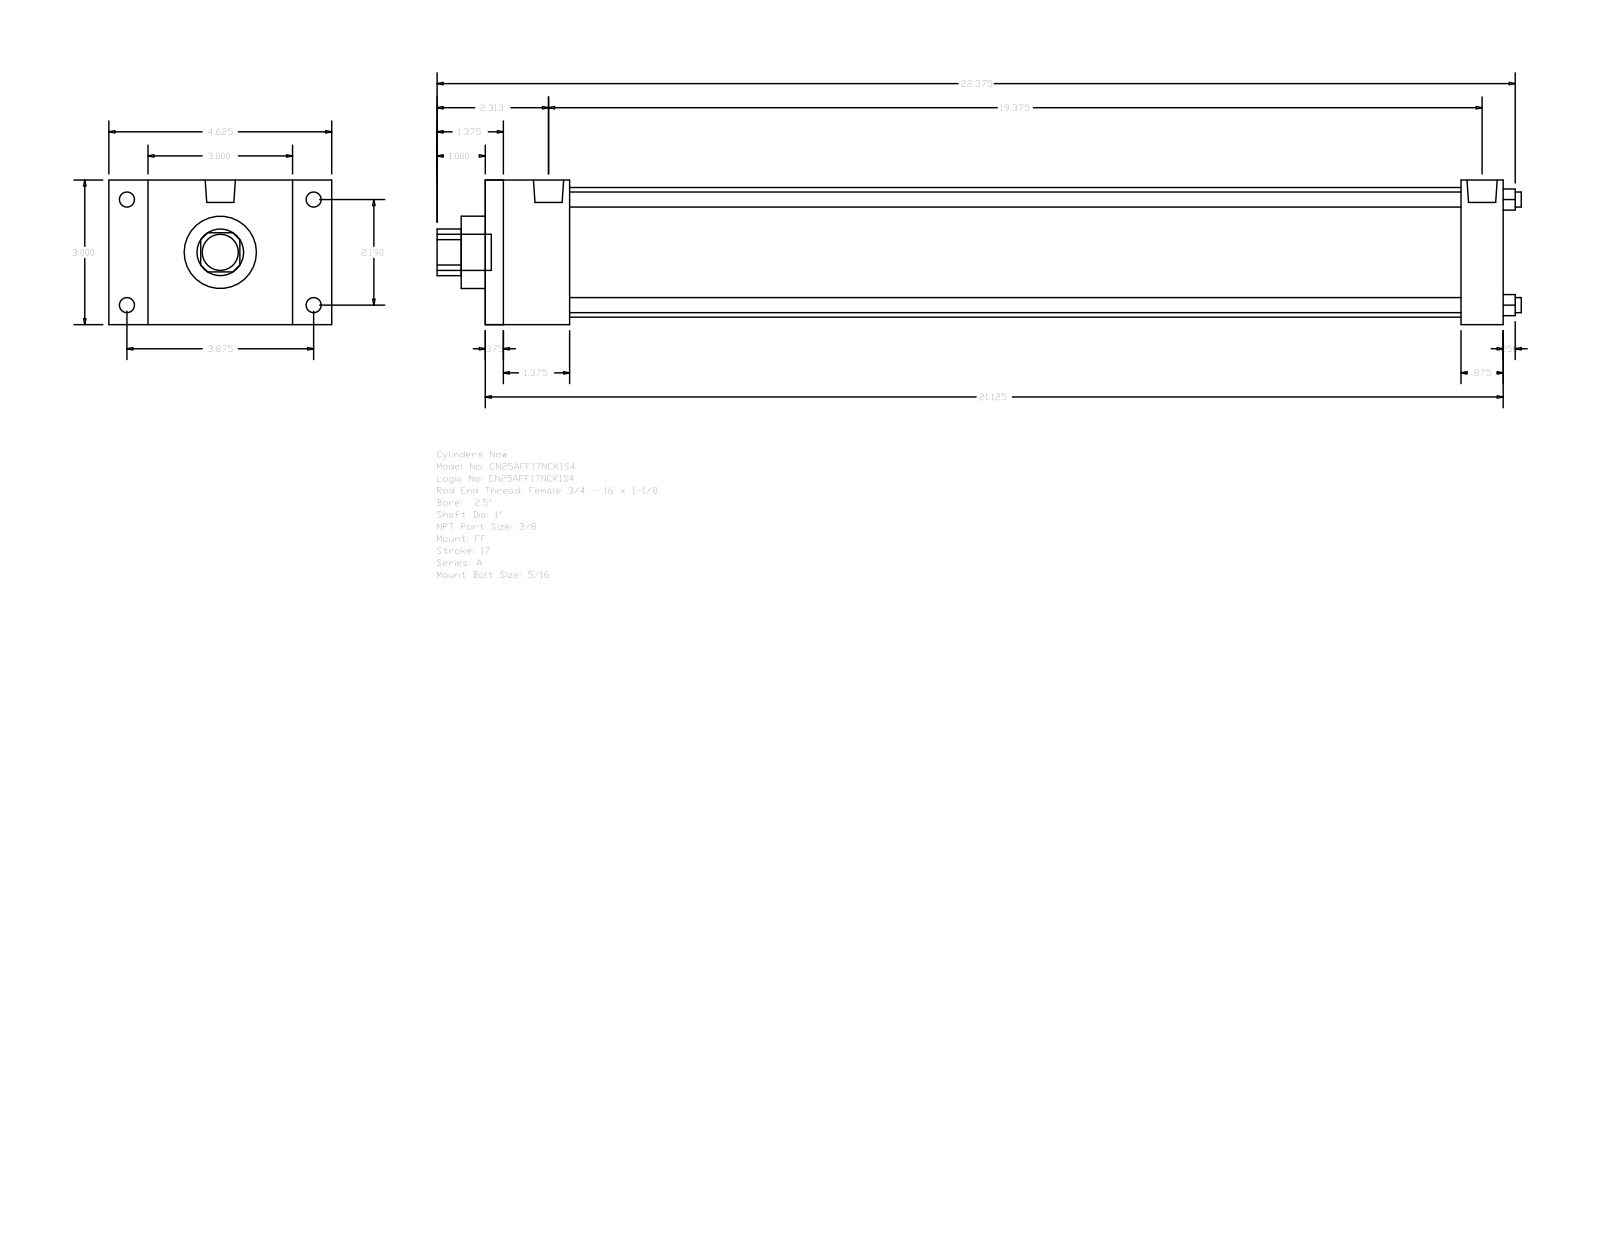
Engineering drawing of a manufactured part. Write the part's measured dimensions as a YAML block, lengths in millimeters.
part_name: "A_FF__0250_1"
step_written_by: "GSSL Pune (CONFIG_CONTROL_DESIGN)"
units: millimeters
bodies: {solids: 0, faces: 92, planar: 64, cylindrical: 28, other: 0}
overall_size: [571.5, 117.47, 76.2]
round_holes:
  - {diameter: 7.94, count: 4}
  - {diameter: 25.4, count: 1}
  - {diameter: 38.1, count: 1}
  - {diameter: 68.33, count: 1}
round_bosses_or_shafts:
  - {diameter: 7.94, count: 4}
  - {diameter: 5.56, count: 4}
  - {diameter: 15.93, count: 2}
  - {diameter: 19.05, count: 1}
partial_cylinders:
  - {radius: 12.29, count: 1}
face_to_face_distances: [76.2, 536.58, 9.52, 527.06, 44.45, 514.35, 34.93, 504.83, 469.9, 492.13]
hole_center_spacings: [39.33, 55.62, 78.66]
